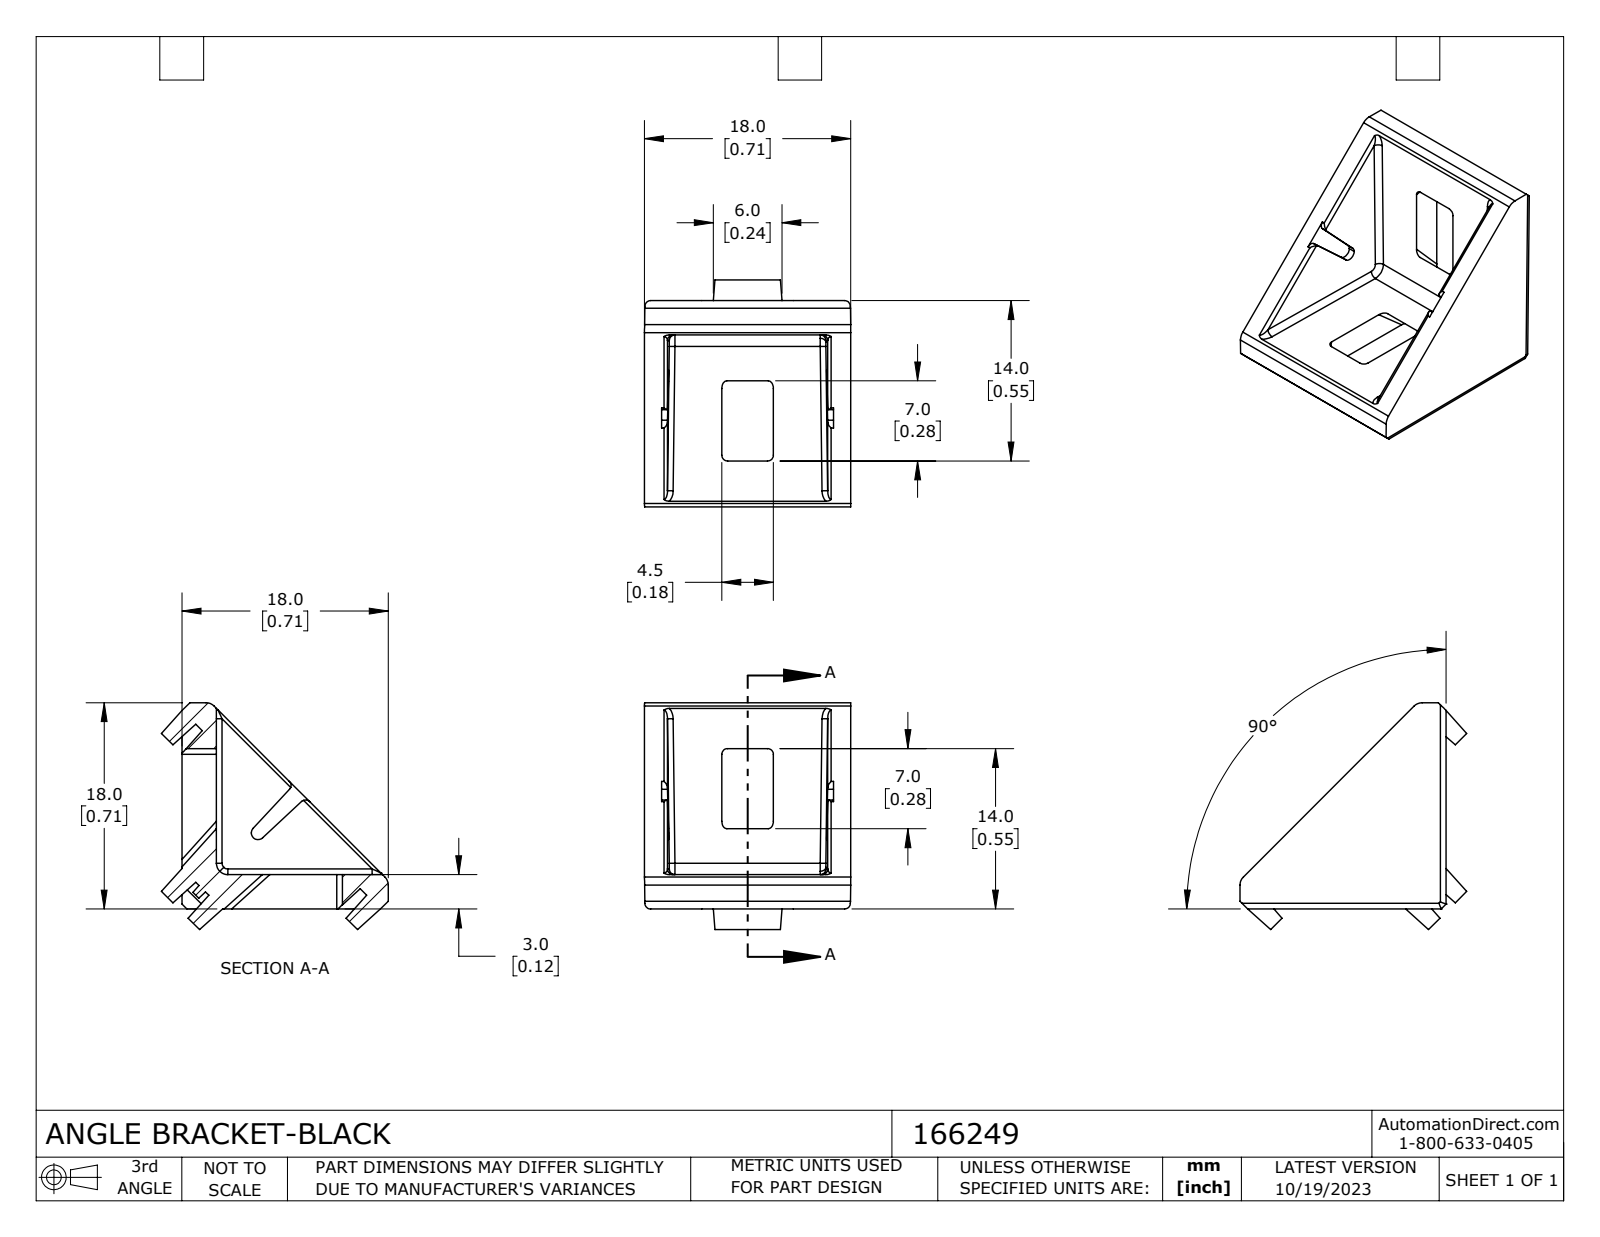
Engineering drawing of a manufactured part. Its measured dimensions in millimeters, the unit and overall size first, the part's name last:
Units: millimetres
Overall size (bounding box): 19.8 × 19.8 × 18
Partial cylindrical surfaces — rounded edges, fillets, slot ends (radius × count): R0.3 ×30, R0.5 ×20, R1 ×3, R0.59 ×1
Main face-to-face distances: 3, 2, 1.5, 15, 18, 16.5, 4, 6.63, 20.26, 13.63
Volume: 1 747 mm³ · Surface area: 2 075 mm²
Bodies: 1 solid, 176 faces (88 planar, 65 cylindrical, 23 other)
Part name (STEP PRODUCT): 166249
STEP written by: SolidWorks 2023 (CONFIG_CONTROL_DESIGN)
